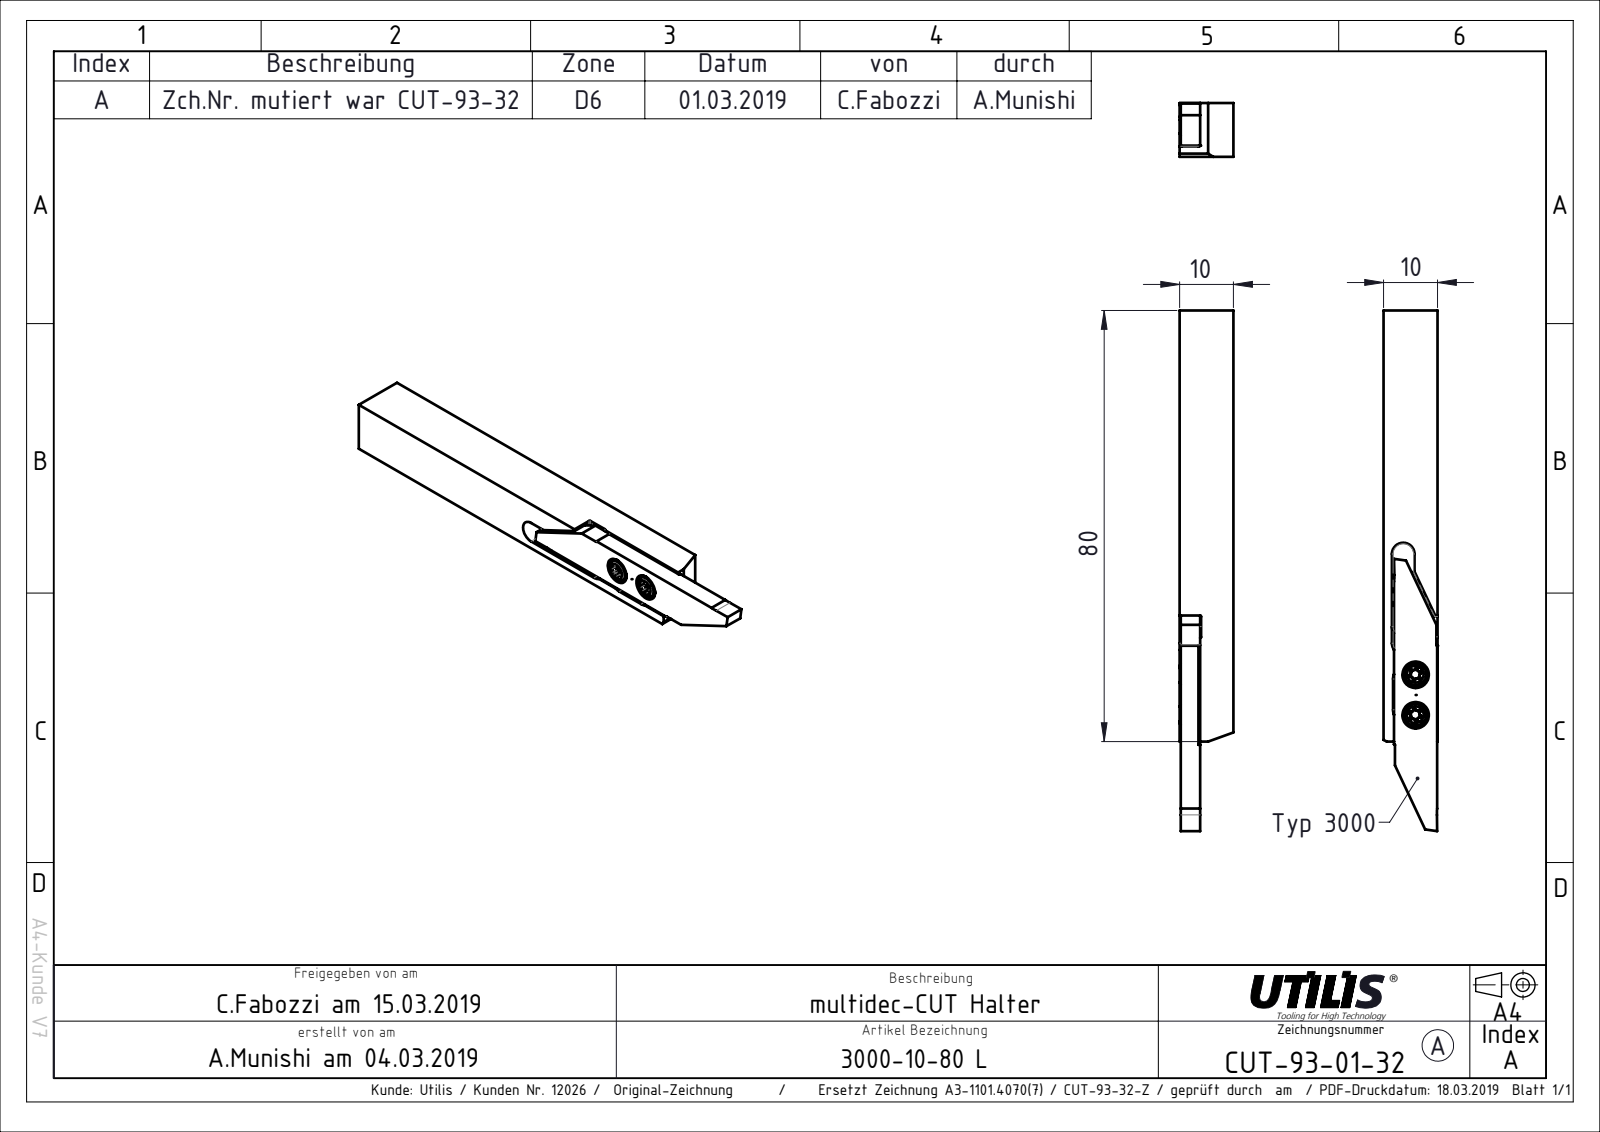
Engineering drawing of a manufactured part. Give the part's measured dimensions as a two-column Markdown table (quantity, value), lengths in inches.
| quantity | value |
| --- | --- |
| part name | CUT-93-32 |
| STEP written by | SolidWorks 2016 (AUTOMOTIVE_DESIGN) |
| units | inches |
| bodies | 1 solid, 45 faces (36 planar, 9 cylindrical, 0 other) |
| overall size | 3.799 × 0.394 × 0.394 |
| volume | 0.497 in³ |
| surface area | 6.284 in² |
| partial cylindrical surfaces (radius × count) | 0.083 × 4, 0.006 × 2, 0.394 × 2 |
| main face-to-face distances | 0.394, 0.386, 0.15, 0.142, 0.244, 0.079, 0.315, 0.061, 0.018, 0.333 |
